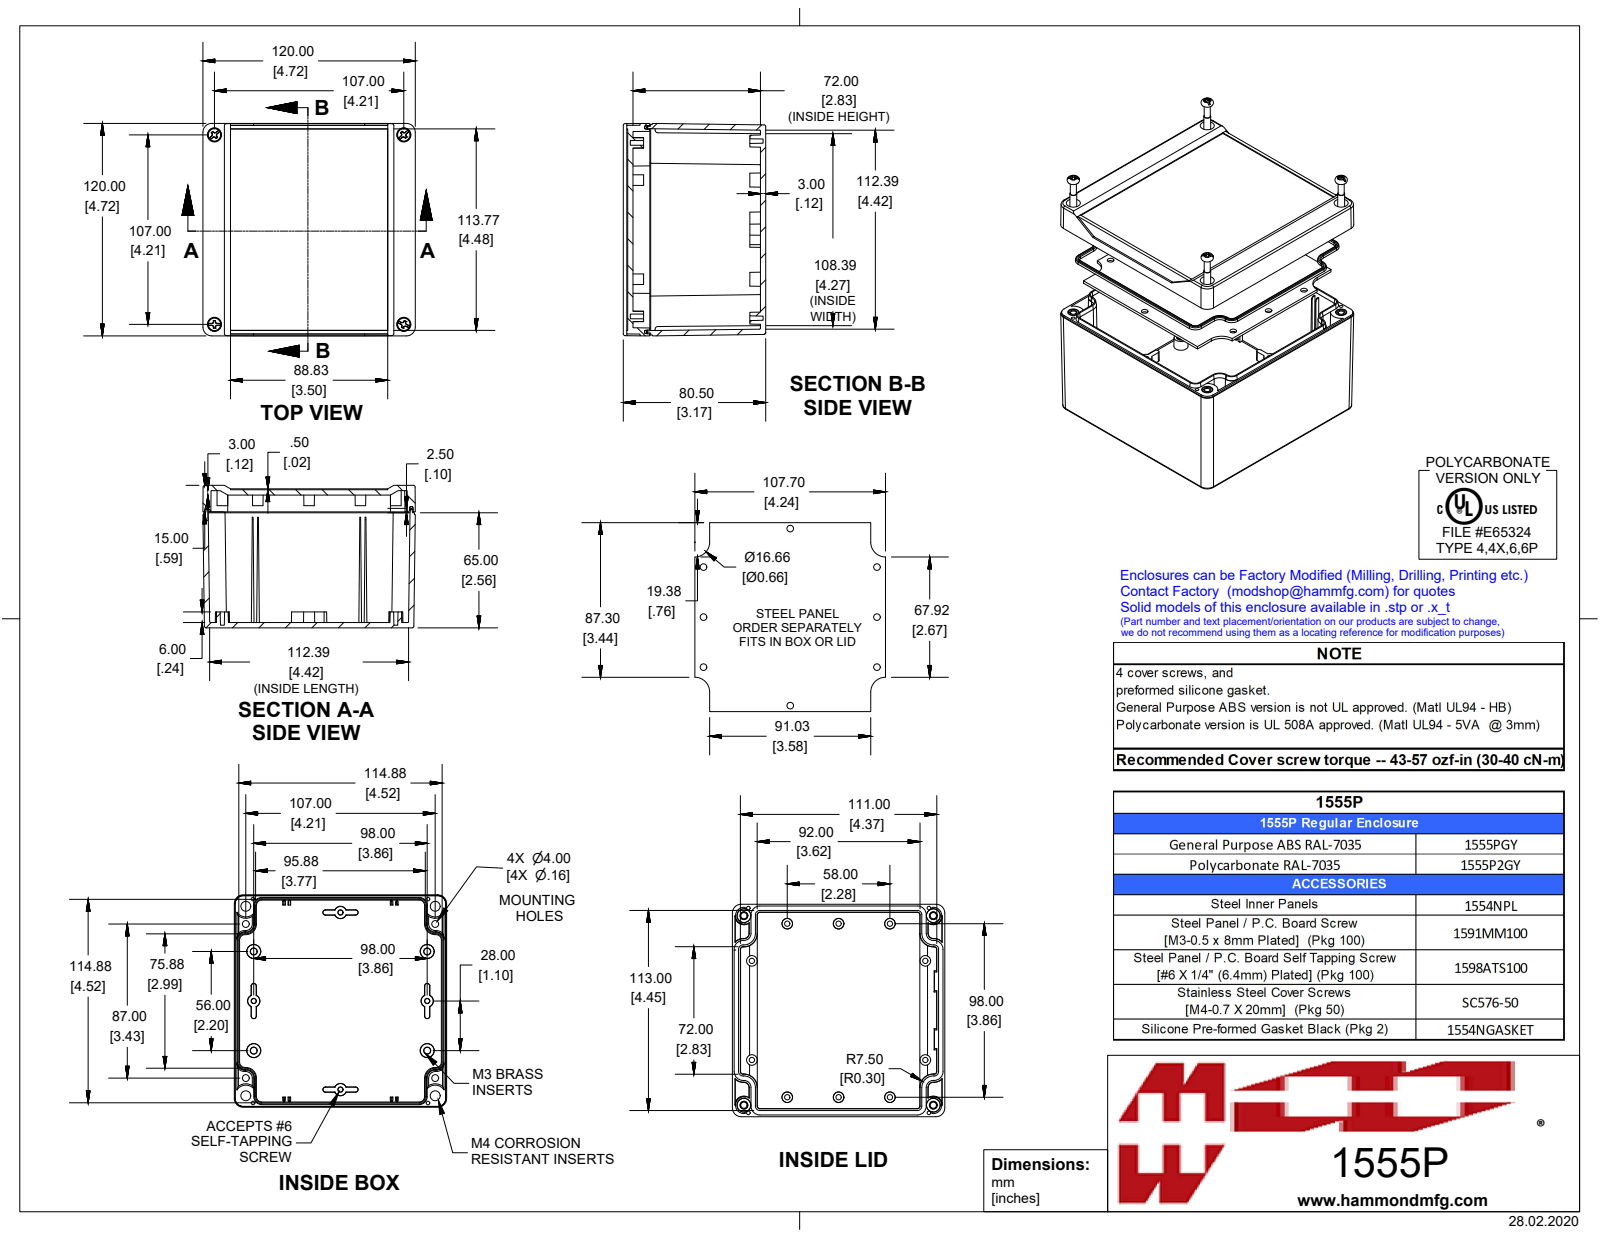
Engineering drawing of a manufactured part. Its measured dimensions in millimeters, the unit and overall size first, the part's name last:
Units: millimetres
Overall size (bounding box): 120 × 120 × 80.5
Round holes (diameter × count): ⌀3 ×10, ⌀2 ×8, ⌀2.5 ×4, ⌀3.3 ×4, ⌀3.5 ×4
Round bosses / shafts (diameter × count): ⌀6.4 ×4, ⌀6 ×4, ⌀5.5 ×4, ⌀5.3 ×4, ⌀4.8 ×4, ⌀3.9 ×4, ⌀3.9 ×4, ⌀3.8 ×4
Partial cylindrical surfaces — rounded edges, fillets, slot ends (radius × count): R0.5 ×40, R1 ×8, R5 ×8, R3.9 ×4, R4.7 ×4, R1.5 ×2
Main face-to-face distances: 3, 75, 78, 72, 1.5, 9.5, 12.5, 11, 2.5, 4.5
Hole centre spacings: 29, 98, 5, 23.7, 24.9, 25.9, 29.9, 51.8
Volume: 218 800 mm³ · Surface area: 159 700 mm²
Bodies: 15 solids, 1398 faces (425 planar, 339 cylindrical, 634 other)
Part name (STEP PRODUCT): 1555P2GY
STEP written by: SolidWorks 2019 (AUTOMOTIVE_DESIGN)
